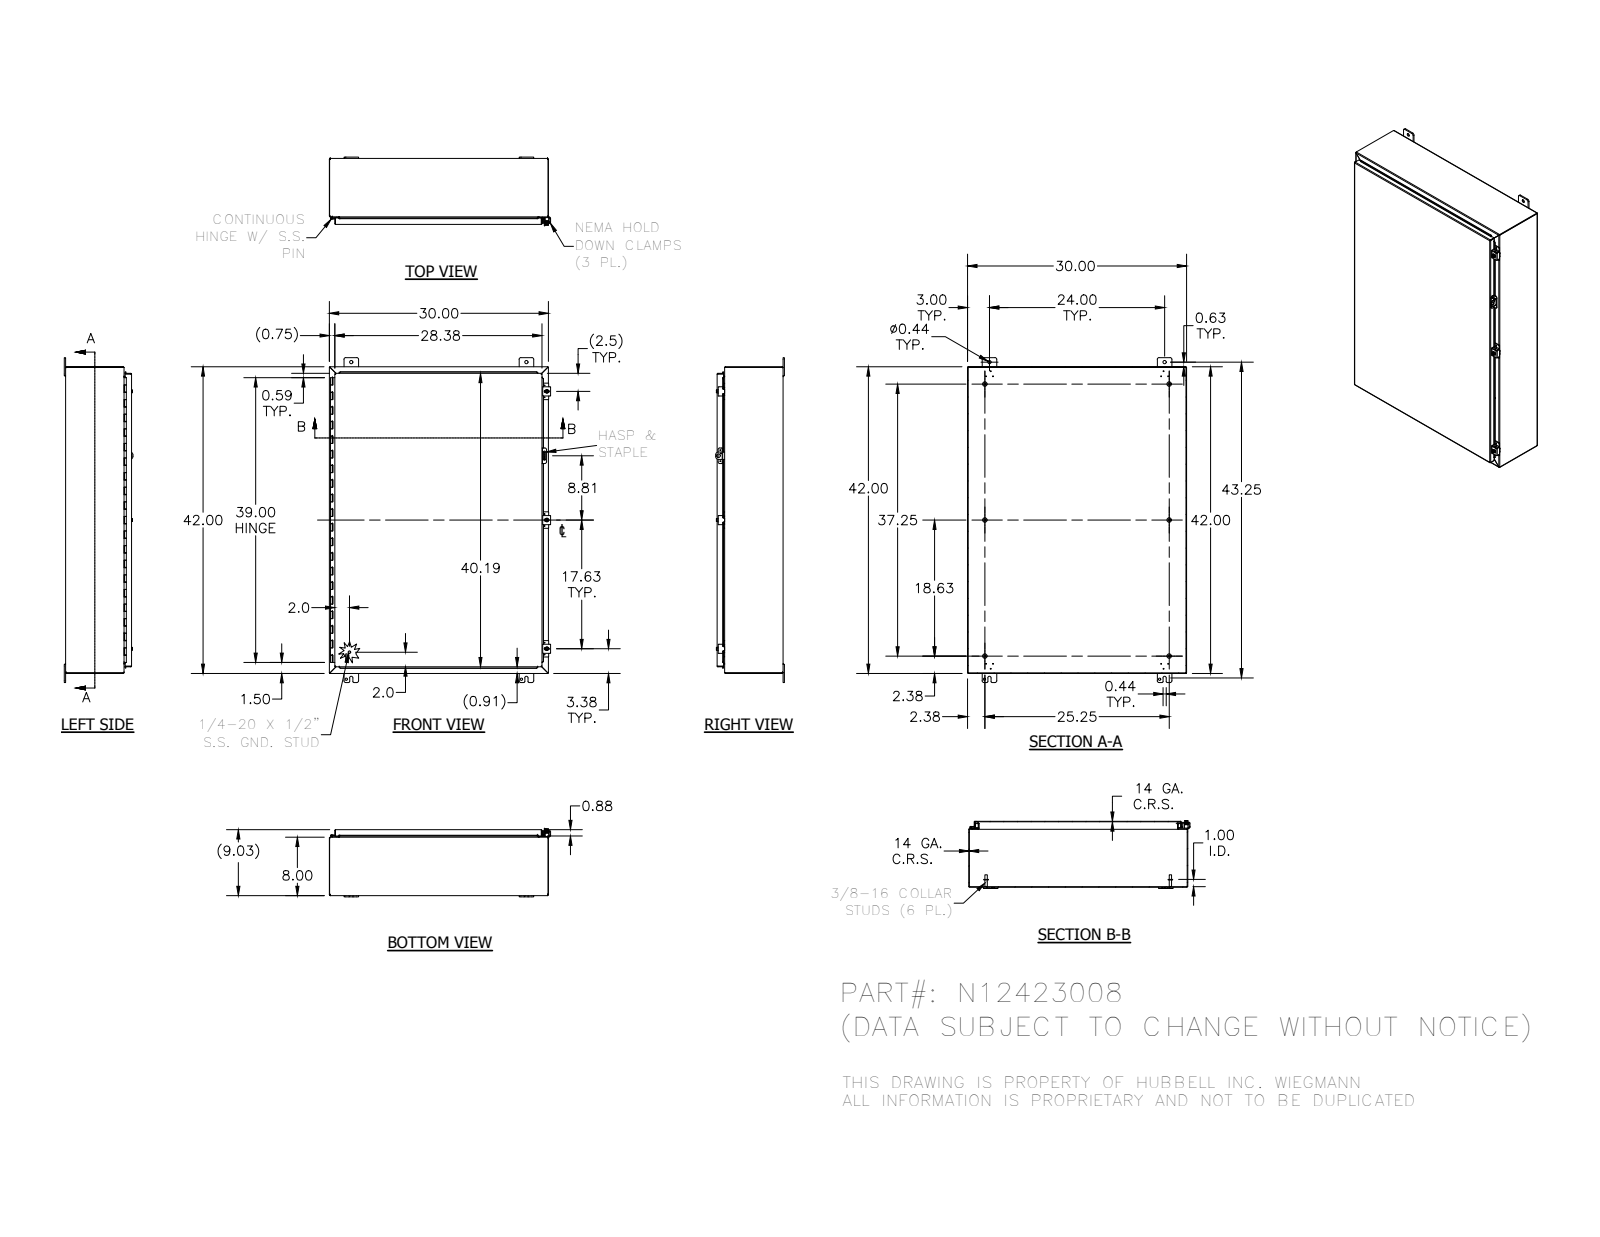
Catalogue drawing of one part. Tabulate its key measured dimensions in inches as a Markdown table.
| quantity | value |
| --- | --- |
| part name | N12423008; 34840; 38420; N12423008BKP (+8 more) |
| STEP written by | Autodesk Inventor 2012 (AUTOMOTIVE_DESIGN) |
| units | inches |
| bodies | 34 solids, 1288 faces (707 planar, 438 cylindrical, 143 other) |
| overall size | 44.5 × 30.311 × 9.41 |
| volume | 319.7 in³ |
| surface area | 8 424 in² |
| round holes (diameter × count) | 0.12 × 12, 0.11 × 9, 0.313 × 4, 0.438 × 4, 0.211 × 3, 0.281 × 3, 0.3 × 3, 0.125 × 1, 0.156 × 1, 0.5 × 1 |
| round bosses / shafts (diameter × count) | 0.625 × 6, 0.33 × 6, 0.25 × 5, 0.52 × 3, 0.5 × 3, 0.35 × 3, 0.115 × 2, 0.337 × 1 |
| partial cylindrical surfaces (radius × count) | 0.03 × 39, 0.063 × 31, 0.125 × 27, 0.25 × 27, 0.031 × 23, 0.105 × 23, 0.07 × 8, 0.1 × 6 |
| main face-to-face distances | 0.074, 8.959, 8.885, 9.033, 29.926, 41.926, 7.926, 1.033, 29.852, 30 |
| hole center spacings | 24, 0.759, 0.839, 0.876, 0.94, 0.969, 1.995, 23.367 |
